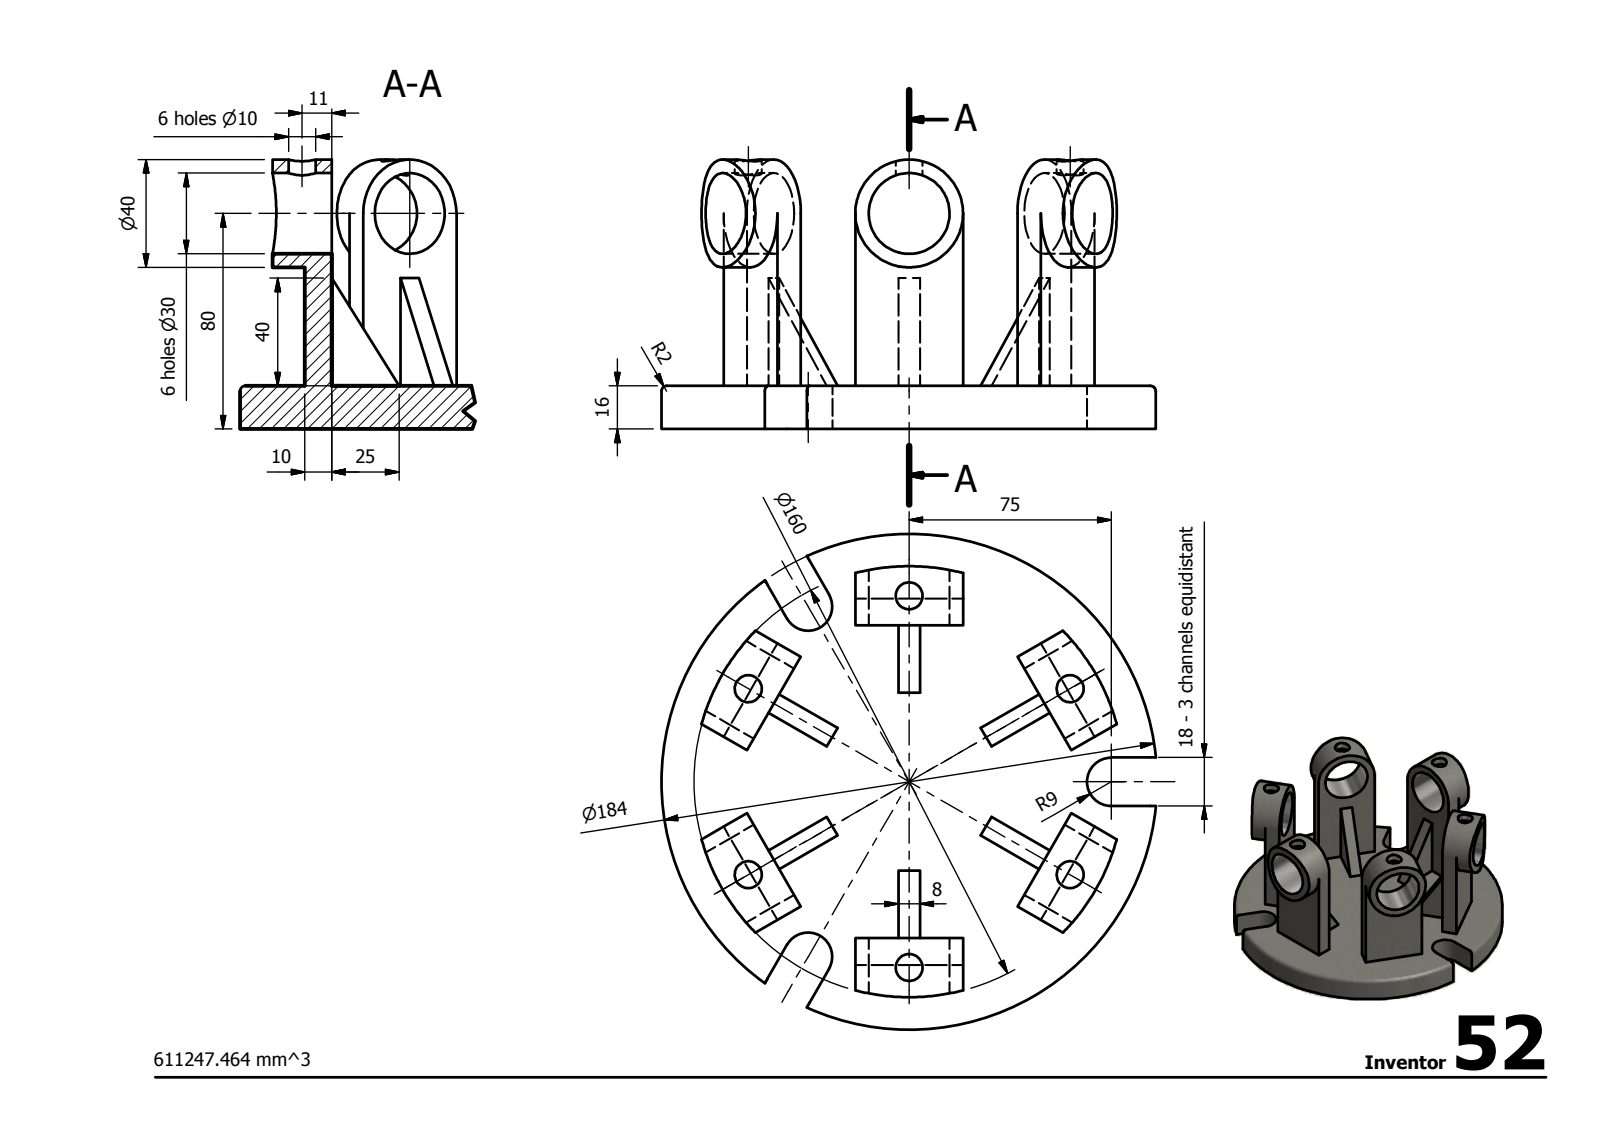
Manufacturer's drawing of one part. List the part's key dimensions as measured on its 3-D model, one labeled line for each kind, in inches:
STEP written by: Autodesk Inventor 2014 (AUTOMOTIVE_DESIGN)
Units: inches
Bodies: 1 solid, 83 faces (50 planar, 30 cylindrical, 3 other)
Overall size (bounding box): 7.244 × 7.227 × 3.937
Volume: 37.3 in³ · Surface area: 194.7 in²
Round holes (diameter × count): ⌀0.394 ×6, ⌀1.181 ×5
Round bosses / shafts (diameter × count): ⌀1.575 ×3, ⌀7.244 ×1
Partial cylindrical surfaces — rounded edges, fillets, slot ends (radius × count): R0.354 ×3, R3.15 ×1
Main face-to-face distances: 0.63, 0.394, 4.961, 4.567, 0.945, 5.354, 1.575, 0.315, 2.323, 3.031
Hole centre spacings: 2.717, 4.705, 4.706, 5.433, 5.433
